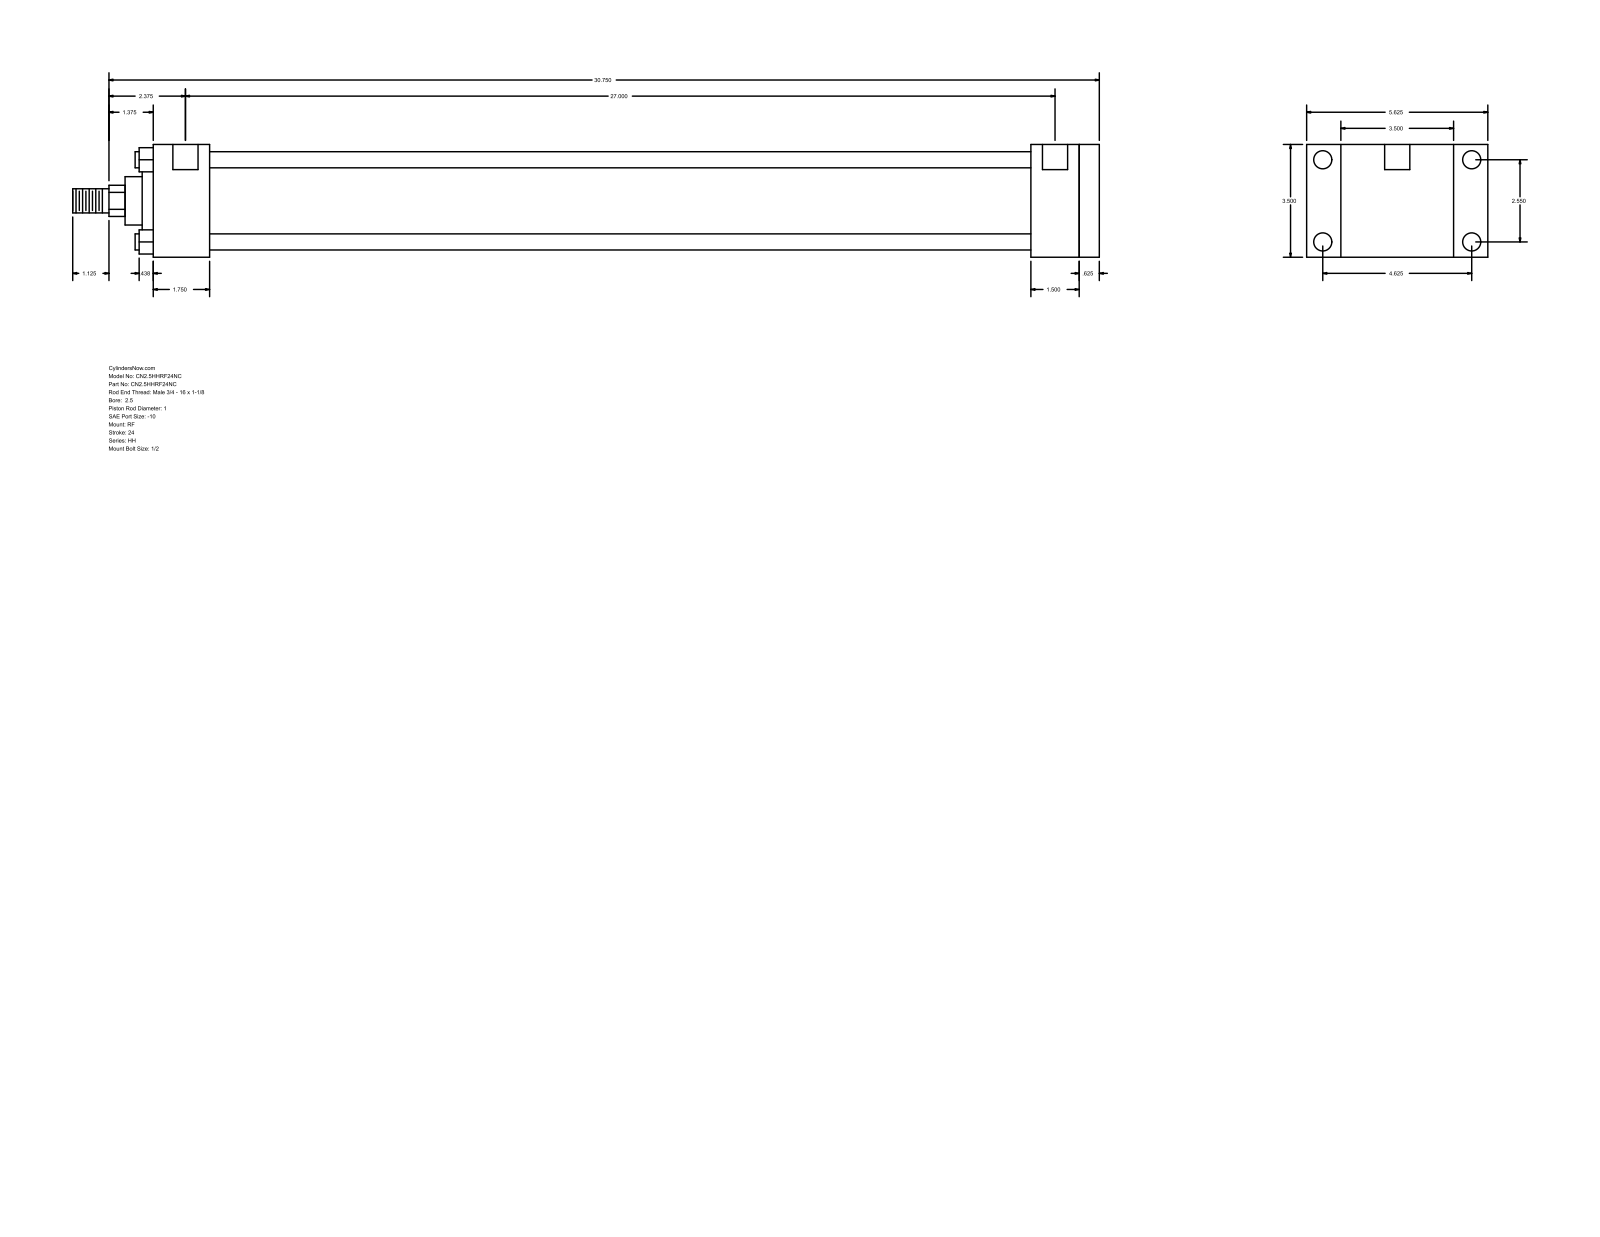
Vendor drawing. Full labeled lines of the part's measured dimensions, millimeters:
Part name (STEP PRODUCT): HH_RF__0250_1
STEP written by: GSSL Pune (CONFIG_CONTROL_DESIGN)
Units: millimetres
Bodies: 0 solids, 94 faces (65 planar, 29 cylindrical, 0 other)
Overall size (bounding box): 809.62 × 142.88 × 88.9
Round holes (diameter × count): ⌀5.56 ×4, ⌀14.3 ×4, ⌀19.84 ×2
Round bosses / shafts (diameter × count): ⌀12.7 ×4, ⌀73.03 ×1, ⌀60.33 ×1, ⌀38.1 ×1, ⌀25.4 ×1, ⌀19.05 ×1
Partial cylindrical surfaces — rounded edges, fillets, slot ends (radius × count): R12.29 ×1
Main face-to-face distances: 88.9, 15.88, 730.25, 746.13, 44.46, 685.79, 701.67, 692.16, 647.7, 38.09
Hole centre spacings: 1.59, 64.76, 117.48, 134.15, 687.38, 688.97, 685.79
